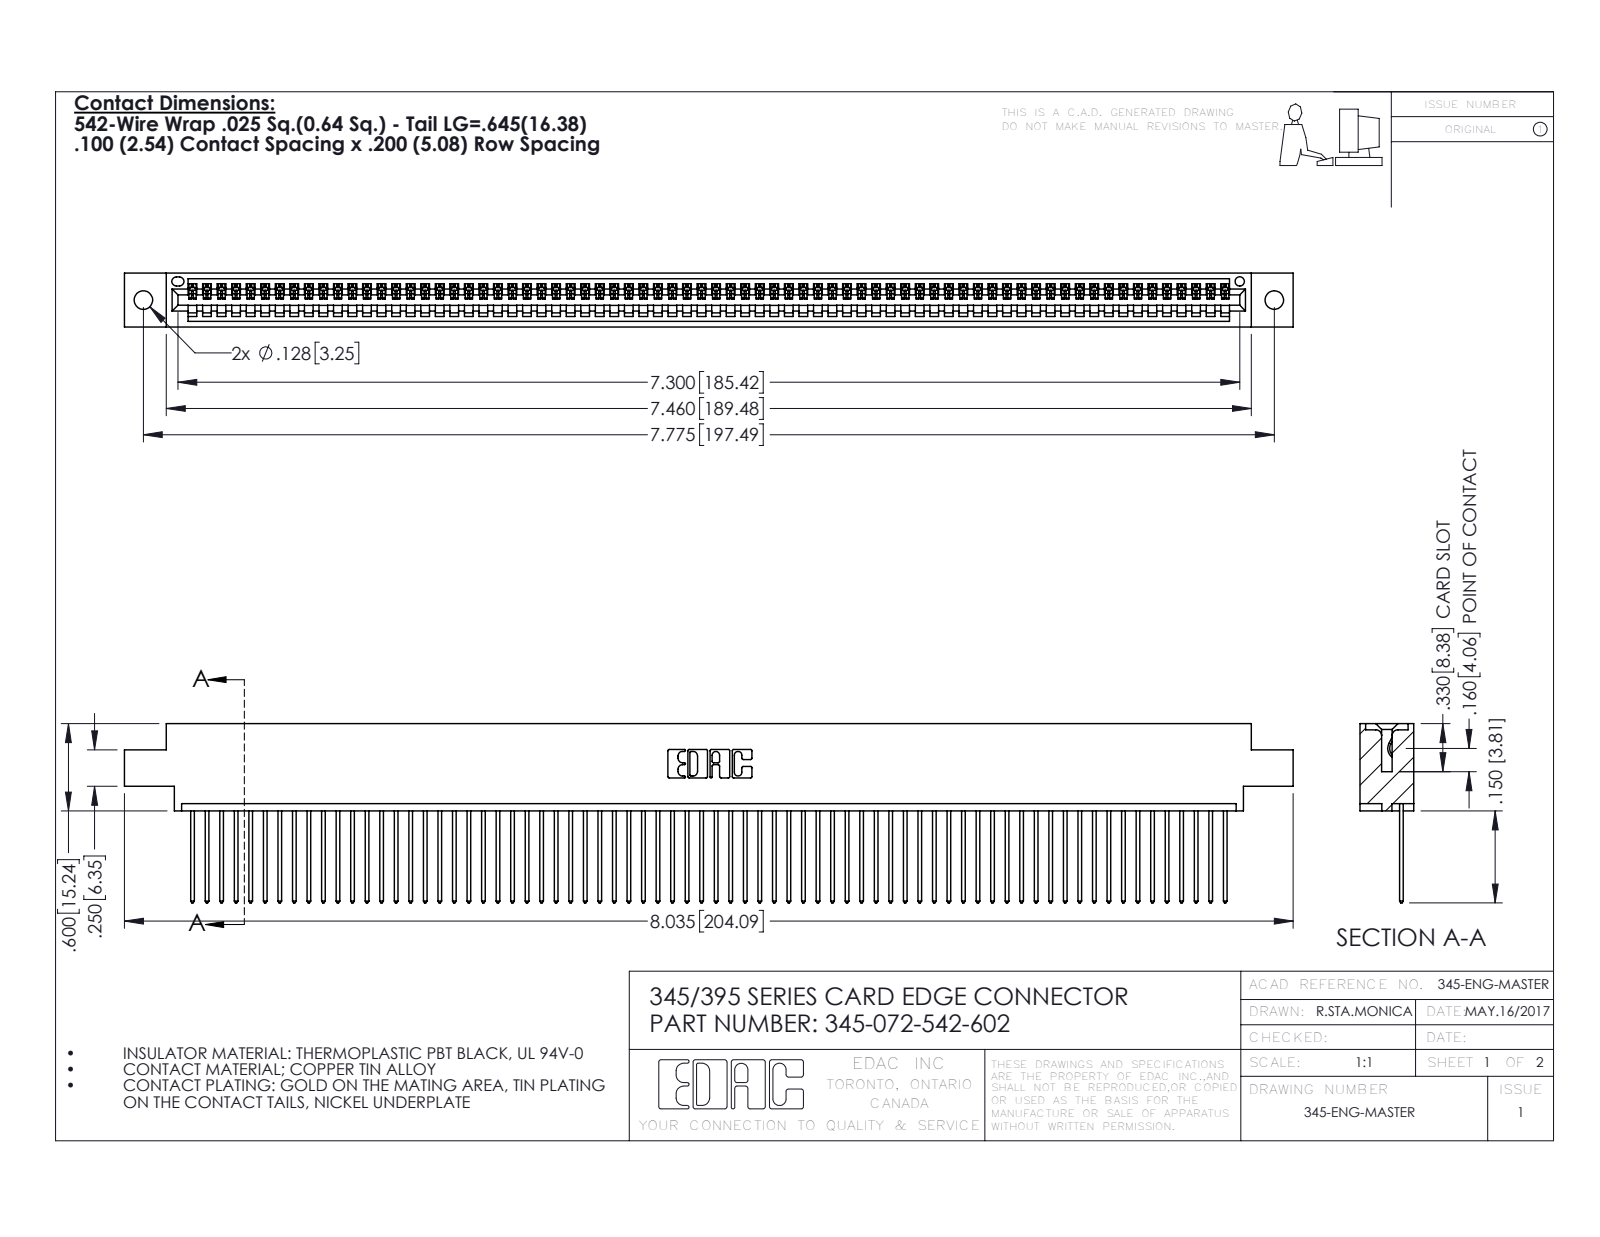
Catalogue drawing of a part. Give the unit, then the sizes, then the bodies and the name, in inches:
Units: inches
Overall size (bounding box): 8.035 × 1.232 × 0.37
Round holes (diameter × count): ⌀0.128 ×2, ⌀0.064 ×1
Partial cylindrical surfaces — rounded edges, fillets, slot ends (radius × count): R0.006 ×144, R0.01 ×144, R0.01 ×22, R0.007 ×6, R0.031 ×6, R0.026 ×3, R0.031 ×2, R0.04 ×2
Main face-to-face distances: 0.072, 0.298, 0.37, 0.098, 0.272, 0.025, 0.2, 0.225, 0.175, 0.149
Hole centre spacings: 0.27, 7.539, 7.775
Volume: 1.199 in³ · Surface area: 42.43 in²
Bodies: 73 solids, 4306 faces (2964 planar, 1342 cylindrical, 0 other)
Part name (STEP PRODUCT): 345-292-001_345-293-142; 345-072-542-602; 345 Part_0.170 Offset - 0.128 Dia
STEP written by: SolidWorks 2016 (CONFIG_CONTROL_DESIGN)
